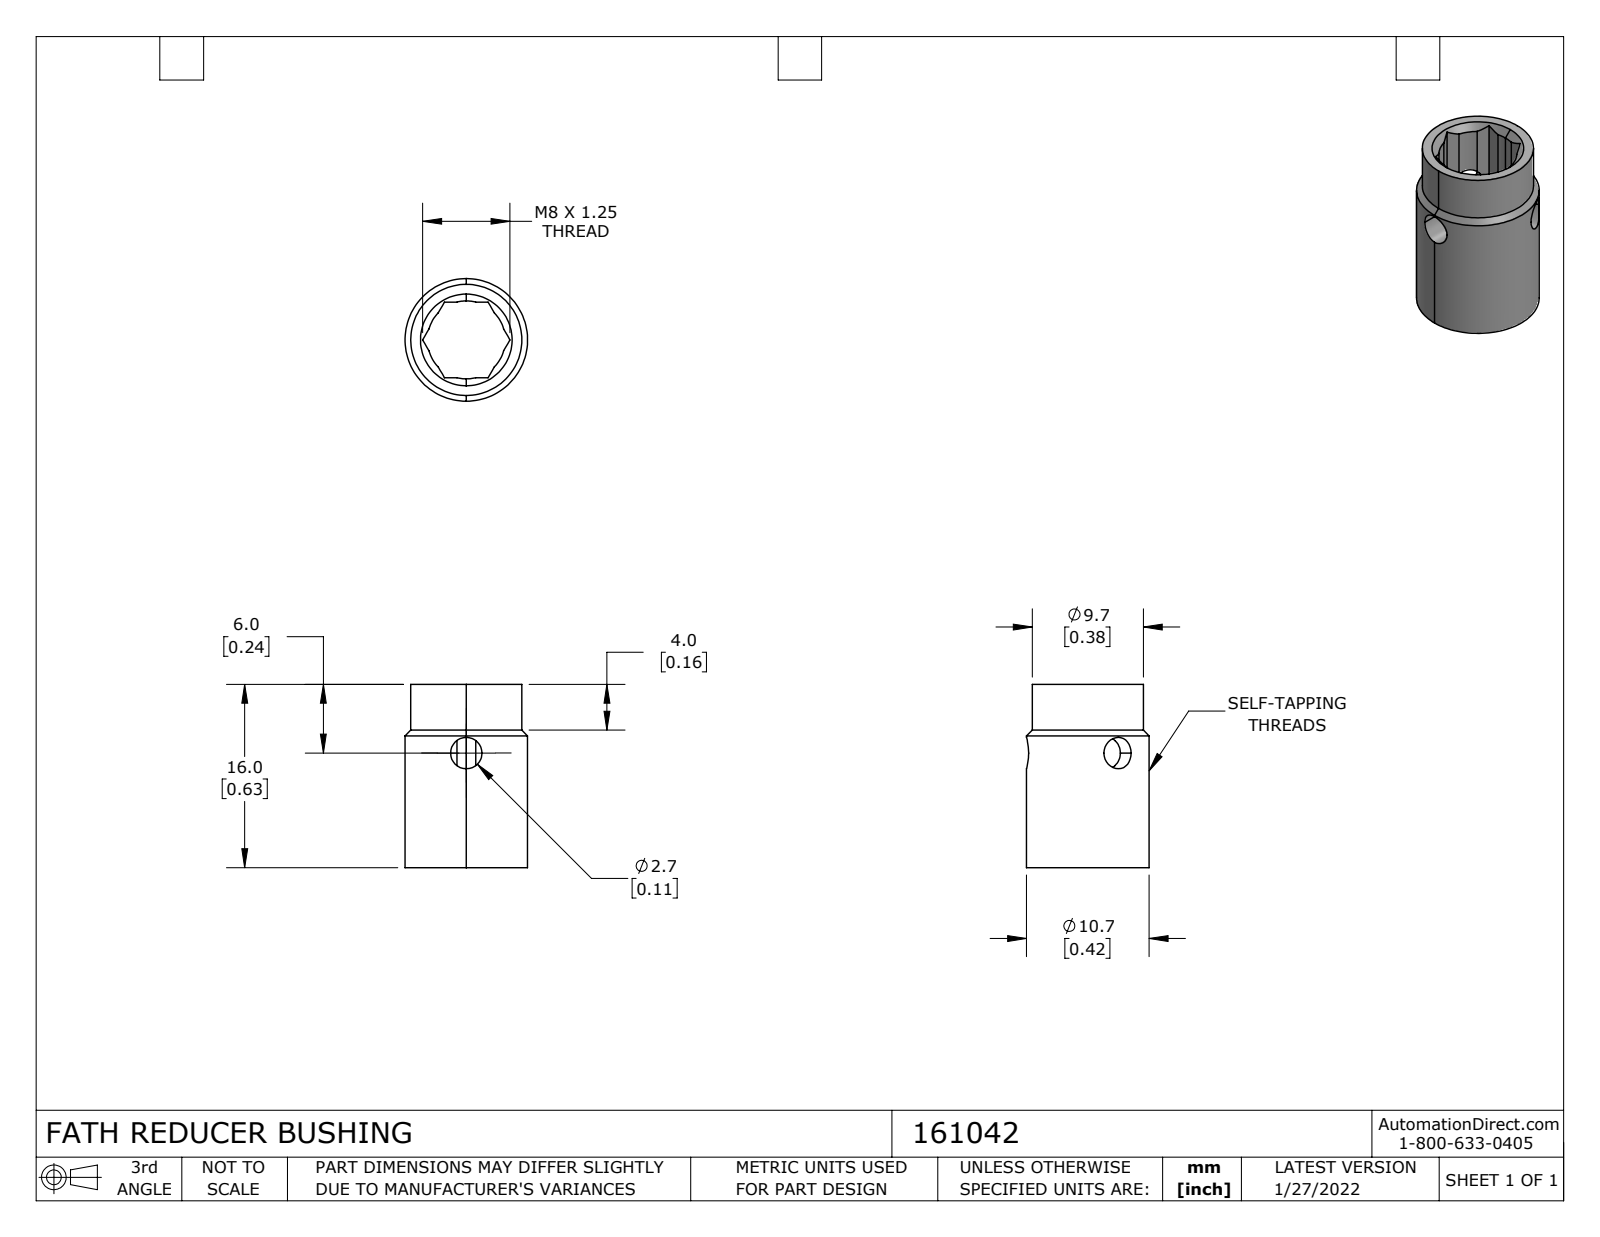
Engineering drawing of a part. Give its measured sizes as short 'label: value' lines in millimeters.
name: 161042
written by: SolidWorks 2021 (CONFIG_CONTROL_DESIGN)
unit: mm
bodies: 1 solid, 40 faces (14 planar, 20 cylindrical, 6 other)
size: 16 × 10.7 × 10.7
volume: 716 mm³; area: 987 mm²
holes: 3× ⌀2.74
bosses: 1× ⌀10.7, 1× ⌀9.7
rounds: 1× R3.4
face distances: 6.6, 16
